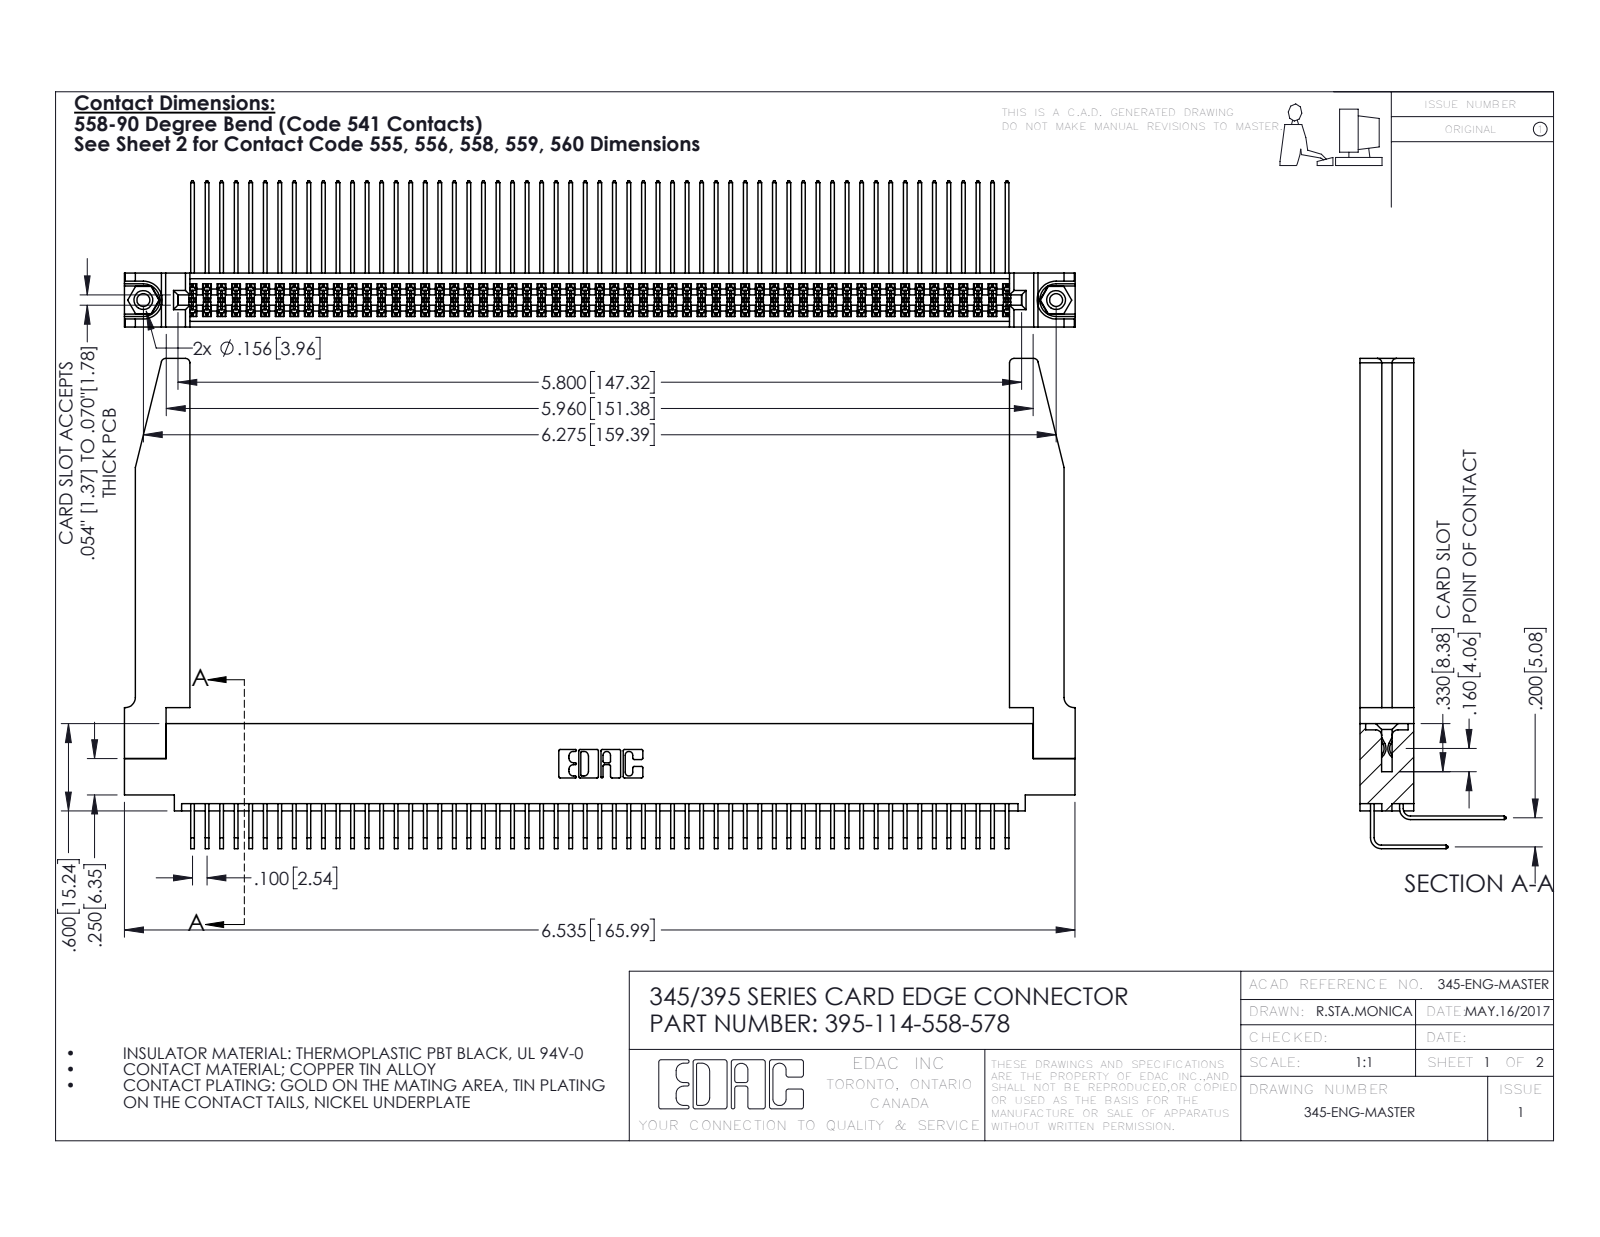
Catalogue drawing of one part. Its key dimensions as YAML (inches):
part_name: "345-250-001_345-250-001-102; 395-114-558-578; 345 Part_0.110 Offset - 0.156 Dia-TH; 345-292-001_558 559 Tail - 1 (+2 more)"
step_written_by: "SolidWorks 2016 (CONFIG_CONTROL_DESIGN)"
units: inches
bodies: {solids: 119, faces: 6292, planar: 4216, cylindrical: 2024, other: 52}
overall_size: [6.536, 3.369, 1.005]
volume: 1.502
surface_area: 54.59
round_holes:
  - {diameter: 0.089, count: 2}
  - {diameter: 0.125, count: 2}
  - {diameter: 0.156, count: 2}
  - {diameter: 0.064, count: 1}
round_bosses_or_shafts:
  - {diameter: 0.155, count: 2}
partial_cylinders:
  - {radius: 0.006, count: 172}
  - {radius: 0.01, count: 22}
  - {radius: 0.03, count: 8}
  - {radius: 0.007, count: 6}
  - {radius: 0.031, count: 6}
  - {radius: 0.026, count: 3}
  - {radius: 0.014, count: 2}
  - {radius: 0.019, count: 2}
face_to_face_distances: [0.072, 0.298, 0.37, 0.2, 0.098, 0.272, 0.025, 0.225, 0.025, 0.175]
hole_center_spacings: [0.27, 6.039, 6.275]
